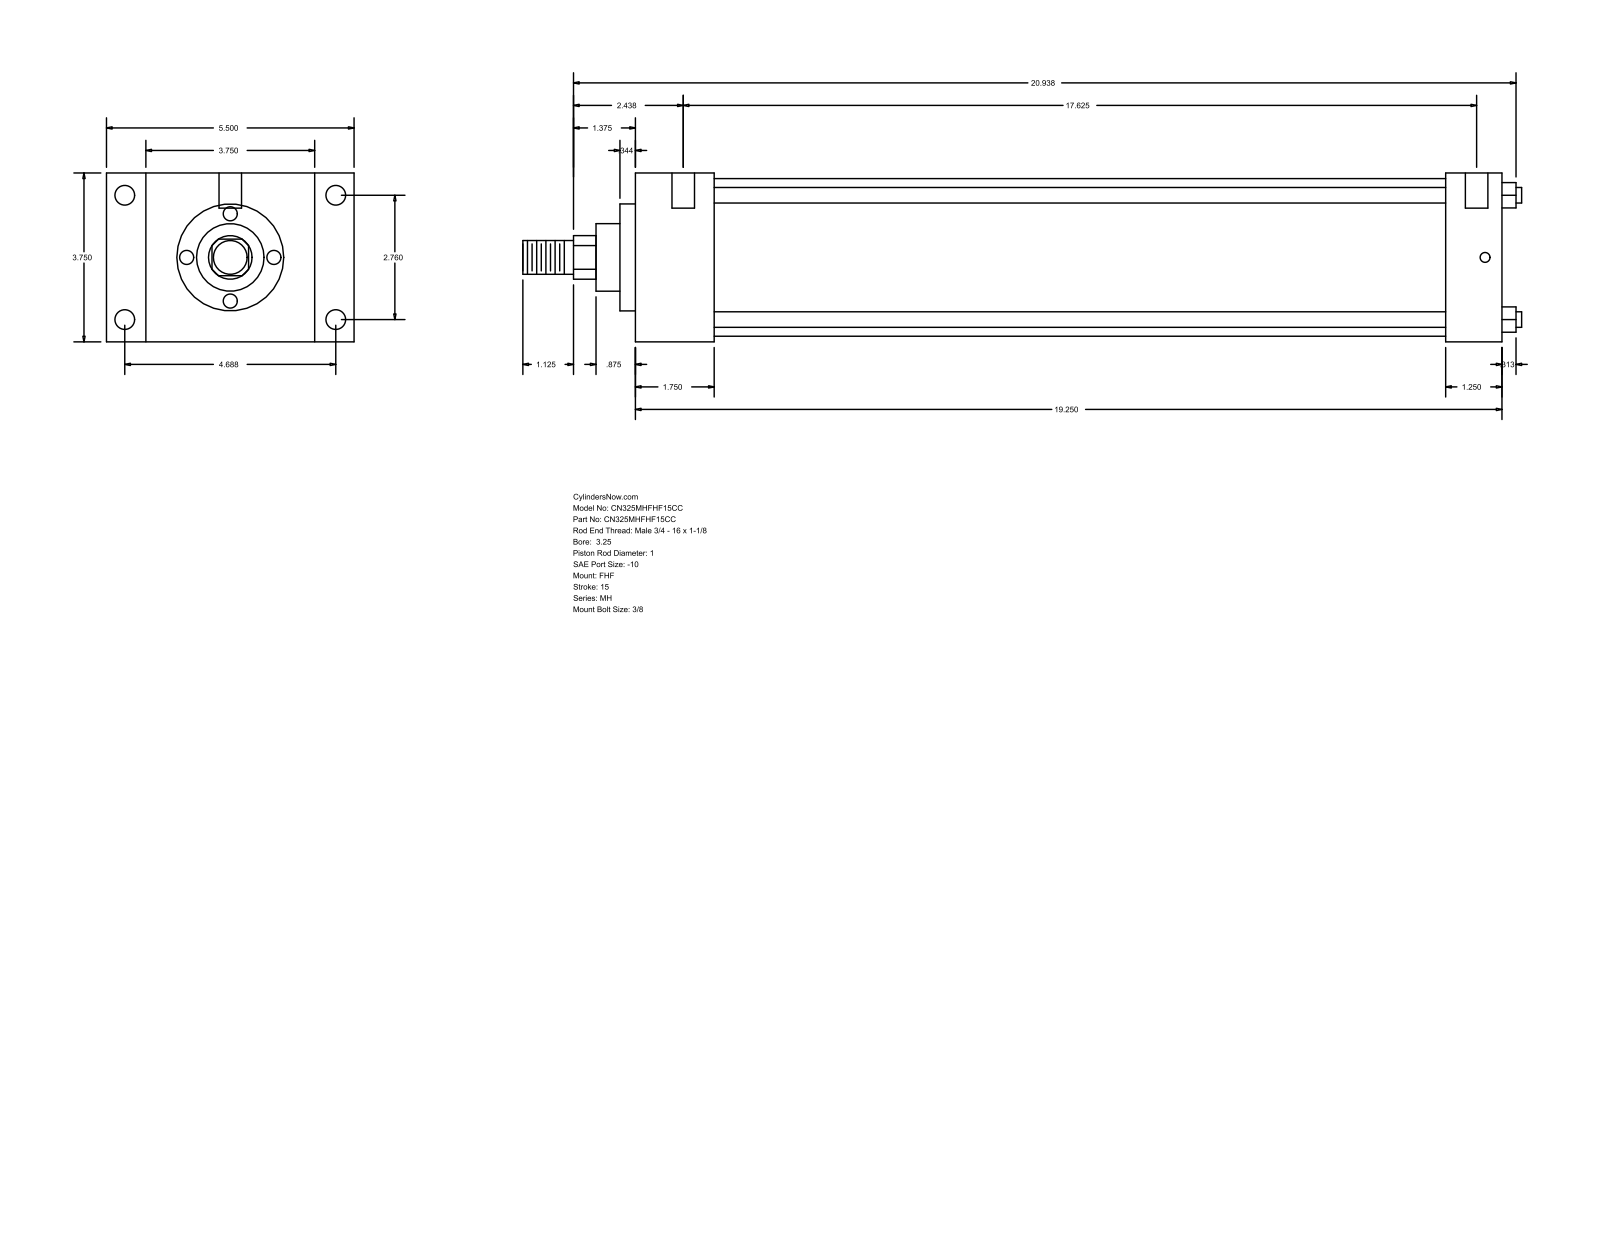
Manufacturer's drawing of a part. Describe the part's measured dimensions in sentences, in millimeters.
The part is named "MH_FHF__0325_1". Its 3-D file was written by "GSSL Pune (CONFIG_CONTROL_DESIGN)". It is 0 solids with 90 faces: 61 planar, 29 cylindrical and 0 other. Overall it measures 563.56 by 139.7 by 95.25 millimeters. Round holes: 4 of diameter 5.56, 4 of diameter 11.13, 2 of diameter 12.7. Round bosses or shafts: 4 of diameter 8.76, 1 of diameter 88.9, 1 of diameter 60.33, 1 of diameter 38.1, 1 of diameter 25.4, 1 of diameter 19.05. Partial cylindrical surfaces (rounded edges, fillets, slot ends): 1 of radius 12.29. The main face-to-face distances are 95.24, 488.96, 44.46, 444.5, 22.23, 117.47, 139.7, 457.2, 412.74, 31.76. The hole center spacings are 70.1, 119.06, 138.16, 454.02, 1.58, 4.76, 447.68, 449.26.
